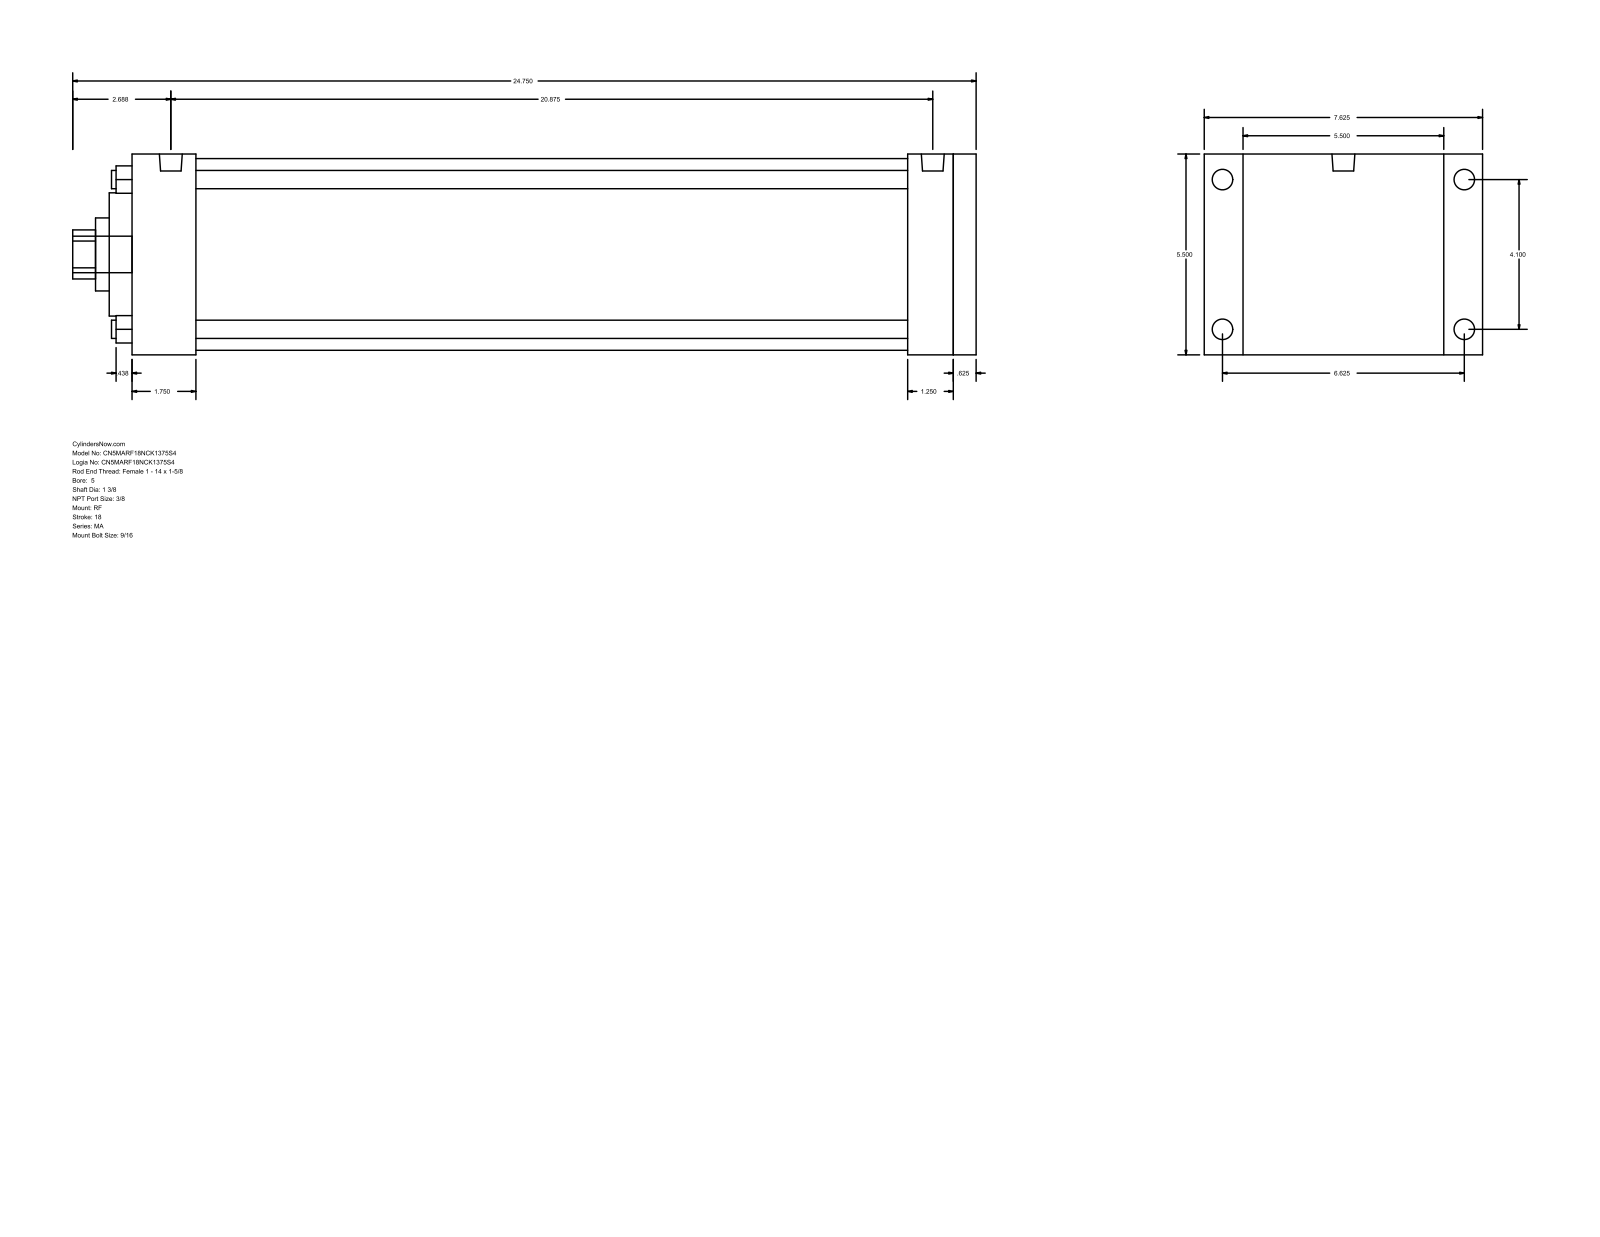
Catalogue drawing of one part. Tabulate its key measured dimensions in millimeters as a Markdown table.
| quantity | value |
| --- | --- |
| part name | MA_RF__0500_1.375 |
| STEP written by | GSSL Pune (CONFIG_CONTROL_DESIGN) |
| units | millimeters |
| bodies | 0 solids, 94 faces (65 planar, 29 cylindrical, 0 other) |
| overall size | 628.65 × 193.68 × 139.7 |
| round holes (diameter × count) | 12.7 × 4, 34.92 × 1, 50.8 × 1, 85.72 × 1, 133.35 × 1 |
| round bosses / shafts (diameter × count) | 14.29 × 4, 11.11 × 4, 15.93 × 2, 25.4 × 1 |
| partial cylindrical surfaces (radius × count) | 17.06 × 1 |
| main face-to-face distances | 139.7, 587.38, 15.88, 571.5, 44.45, 527.05, 542.93, 539.75, 495.3, 31.75 |
| hole center spacings | 73.64, 104.14, 147.28 |
